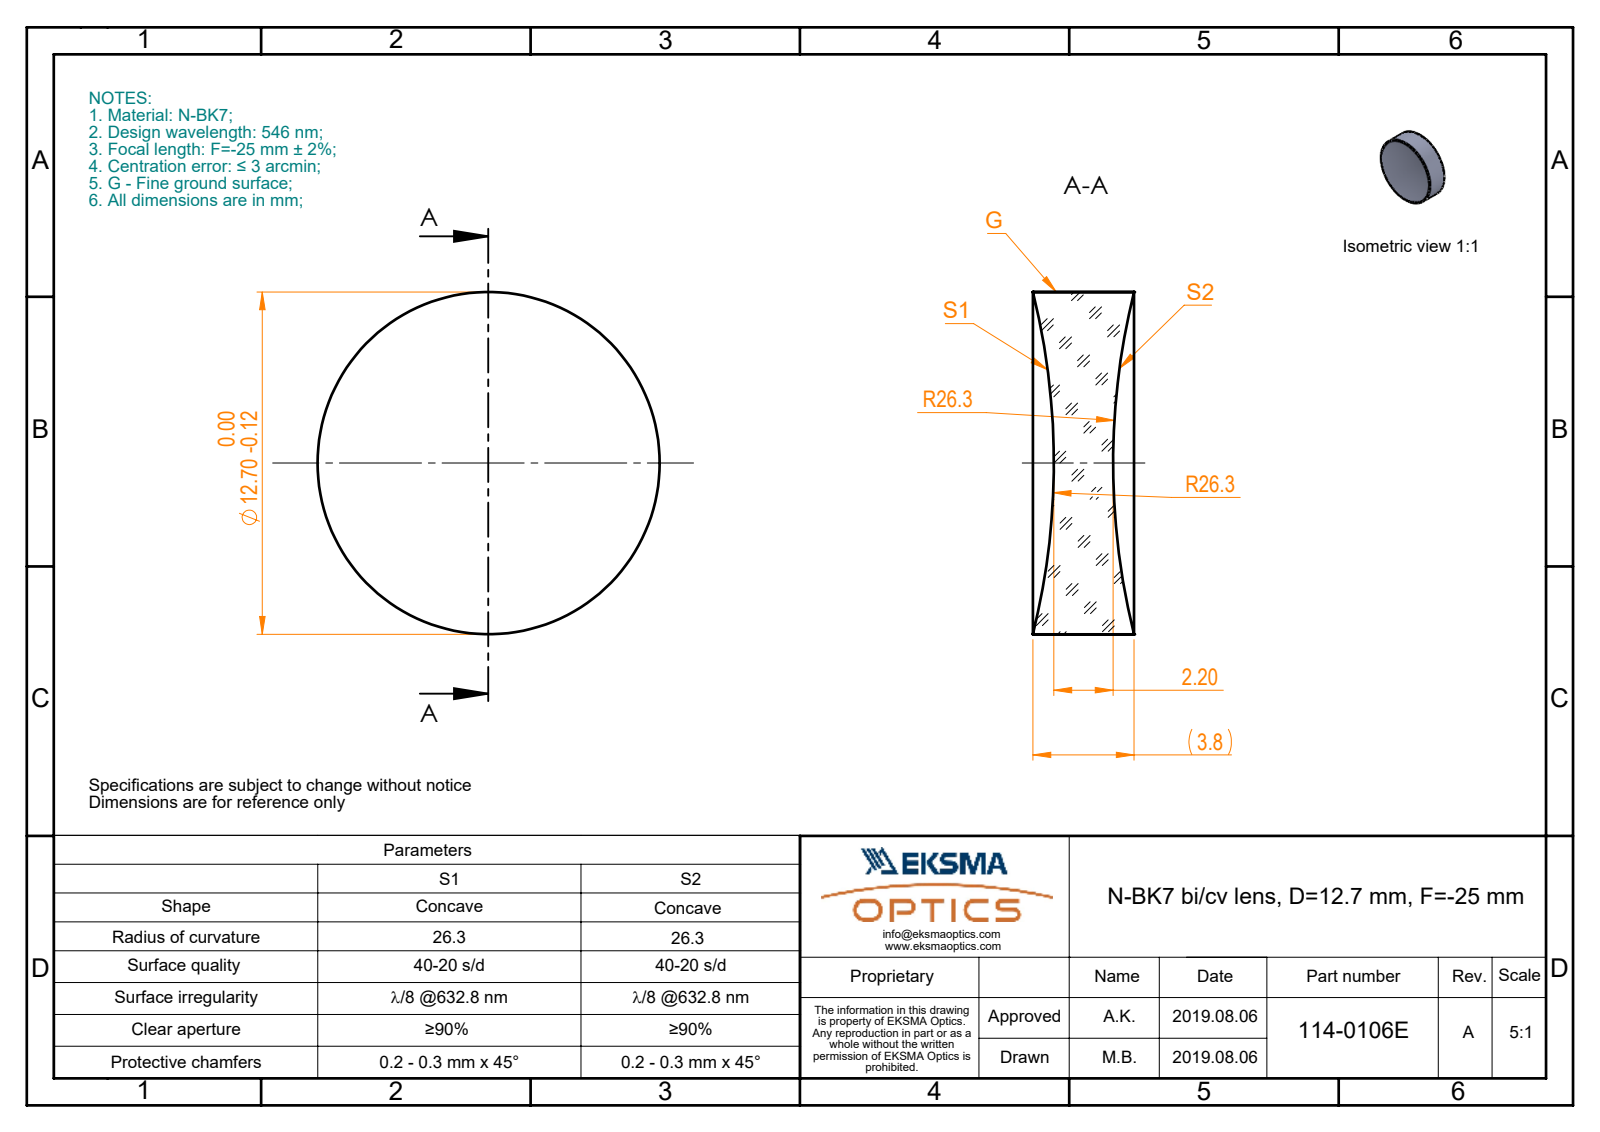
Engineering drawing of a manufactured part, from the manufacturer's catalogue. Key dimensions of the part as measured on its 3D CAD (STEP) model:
Part name (STEP PRODUCT): 114-0106E BK7 bi-cv 12.7 F-25
STEP written by: SolidWorks 2017 (CONFIG_CONTROL_DESIGN)
Units: millimetres
Bodies: 1 solid, 6 faces (0 planar, 2 cylindrical, 4 other)
Overall size (bounding box): 12.7 × 12.7 × 3.76
Volume: 377 mm³ · Surface area: 407 mm²
Round bosses / shafts (diameter × count): ⌀12.7 ×1
